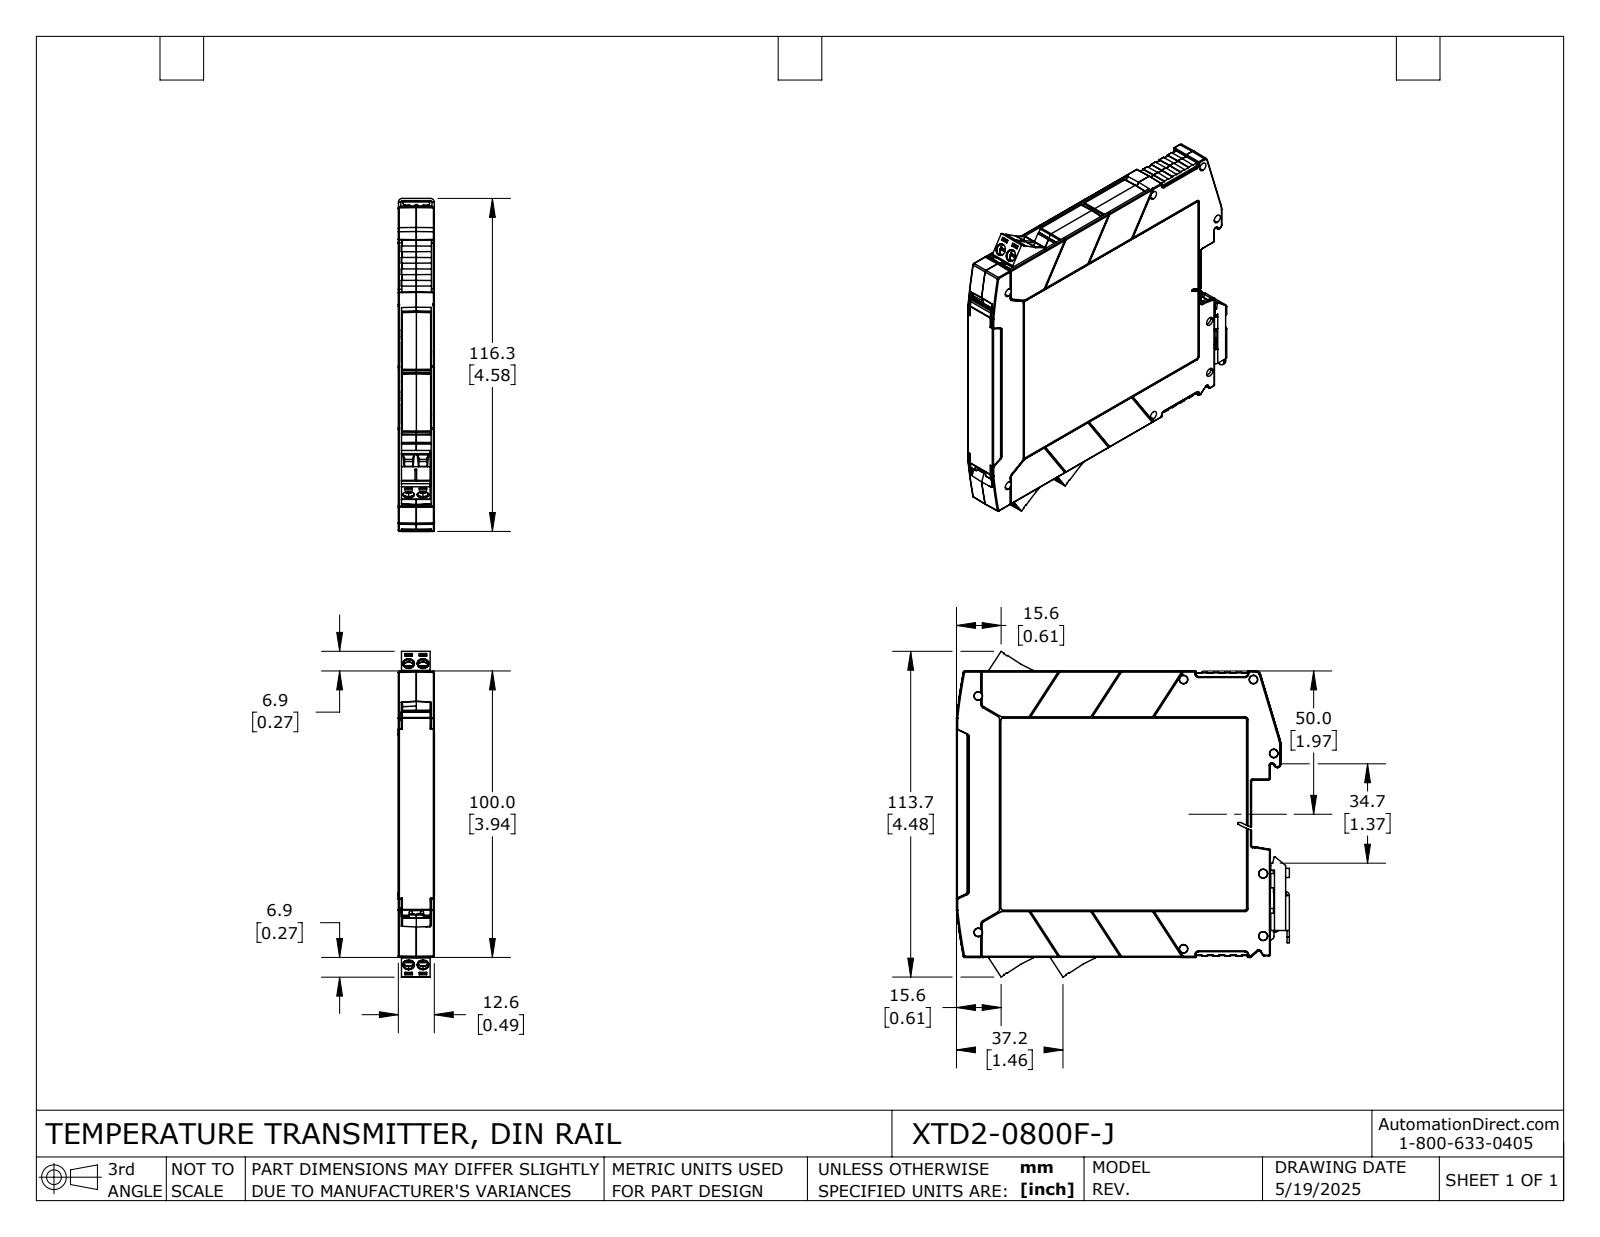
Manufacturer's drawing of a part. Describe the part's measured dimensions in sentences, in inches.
The part is named "XTD2-0800F-J". Its 3-D file was written by "SolidWorks 2024 (AUTOMOTIVE_DESIGN)". It is 14 solids with 3337 faces: 1910 planar, 596 cylindrical and 831 other. Overall it measures 4.577 by 4.478 by 0.496 inches. Its volume is 2.41 cubic inches and its surface area 101.5 square inches. Round holes: 6 of diameter 0.063, 6 of diameter 0.11, 6 of diameter 0.152, 6 of diameter 0.159. Round bosses or shafts: 6 of diameter 0.156, 6 of diameter 0.098, 2 of diameter 0.059, 2 of diameter 0.053. Partial cylindrical surfaces (rounded edges, fillets, slot ends): 89 of radius 0.008, 78 of radius 0.012, 71 of radius 0.02, 22 of radius 0.039, 20 of radius 0.004, 13 of radius 0.016, 12 of radius 0.006, 8 of radius 0.028. The main face-to-face distances are 0.049, 0.445, 0.494, 0.396, 0.043, 0.451, 0.402, 0.031, 0.198, 0.247. The hole center spacings are 0.197, 0.464, 0.504, 0.713, 0.739.
